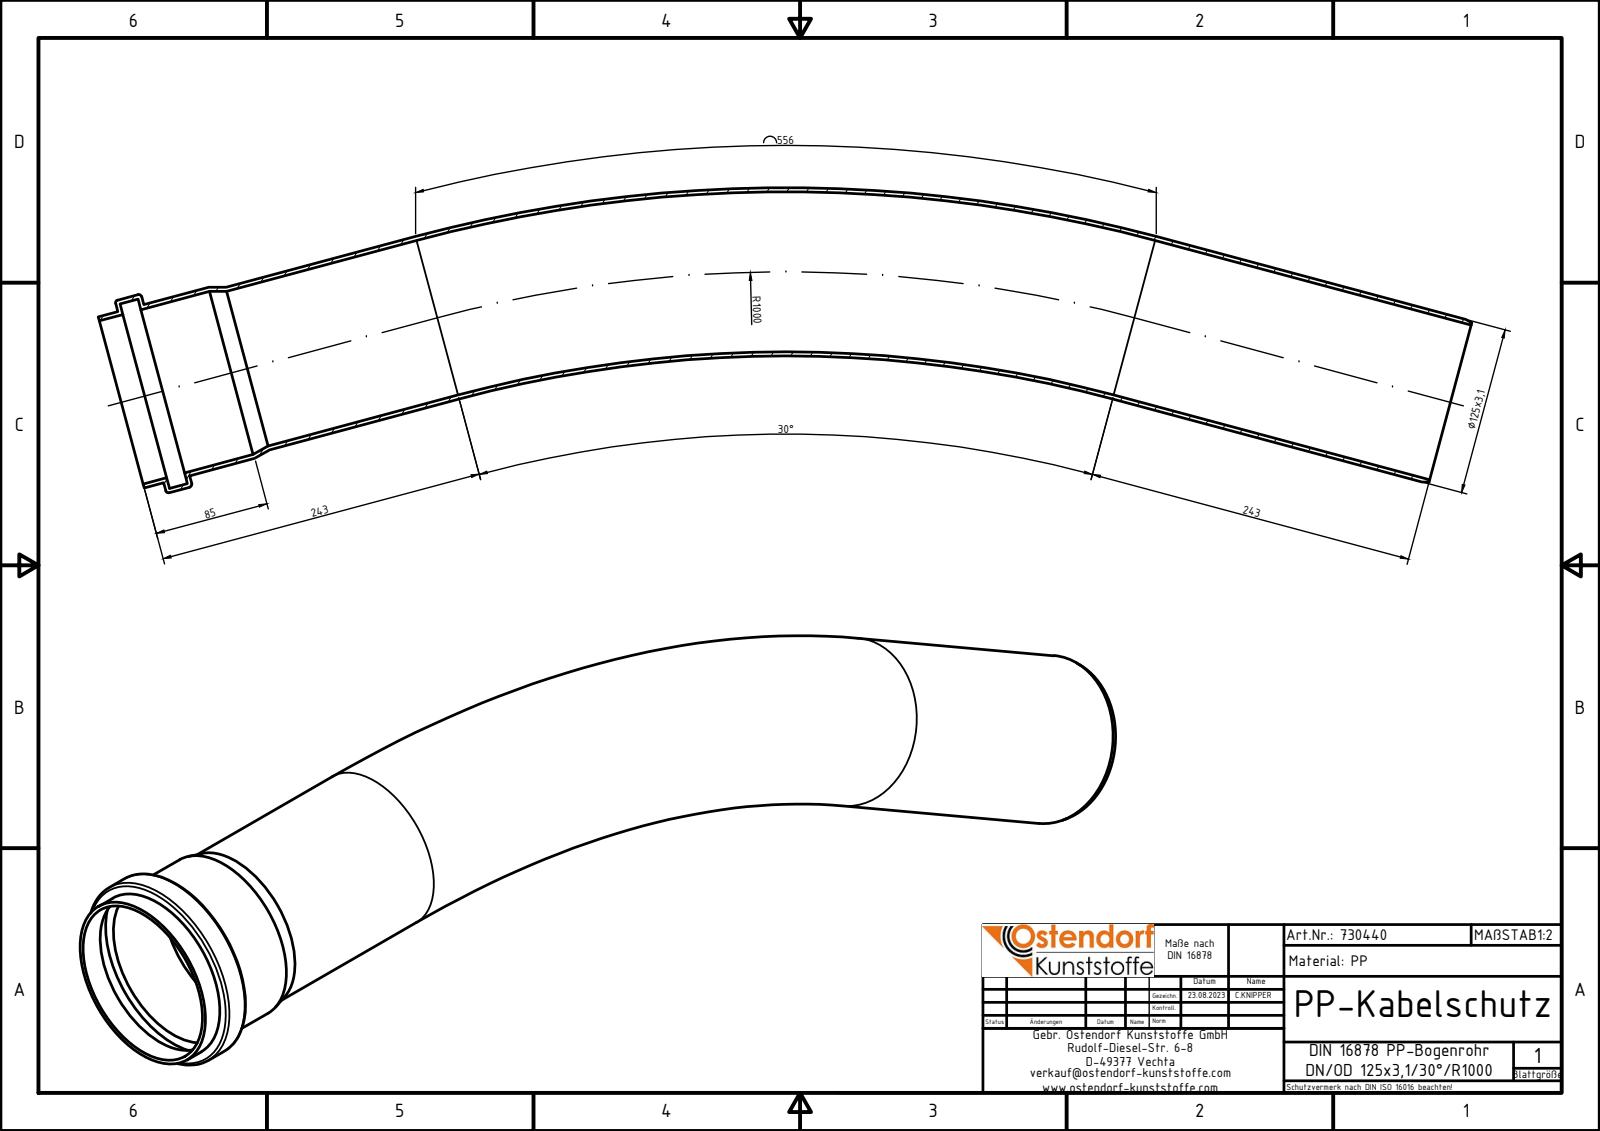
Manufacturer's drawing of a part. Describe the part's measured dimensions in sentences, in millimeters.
The part is named "PP-Bogenrohr_125x31_R1000_30_SM_35018_730440". Its 3-D file was written by "Autodesk Inventor 2024 (AUTOMOTIVE_DESIGN)". It is 1 solid with 23 faces: 6 planar, 10 cylindrical and 7 other. Overall it measures 984.02 by 382.44 by 148 millimeters. Its volume is 1 227 000 cubic millimeters and its surface area 794 377 square millimeters. Round holes: 2 of diameter 118.8, 1 of diameter 125.4, 1 of diameter 141.8. Round bosses or shafts: 2 of diameter 125, 1 of diameter 148, 1 of diameter 131.6. The main face-to-face distances are 3.1, 16.9, 13.8, 20, 15, 18.1, 31.9, 35.
